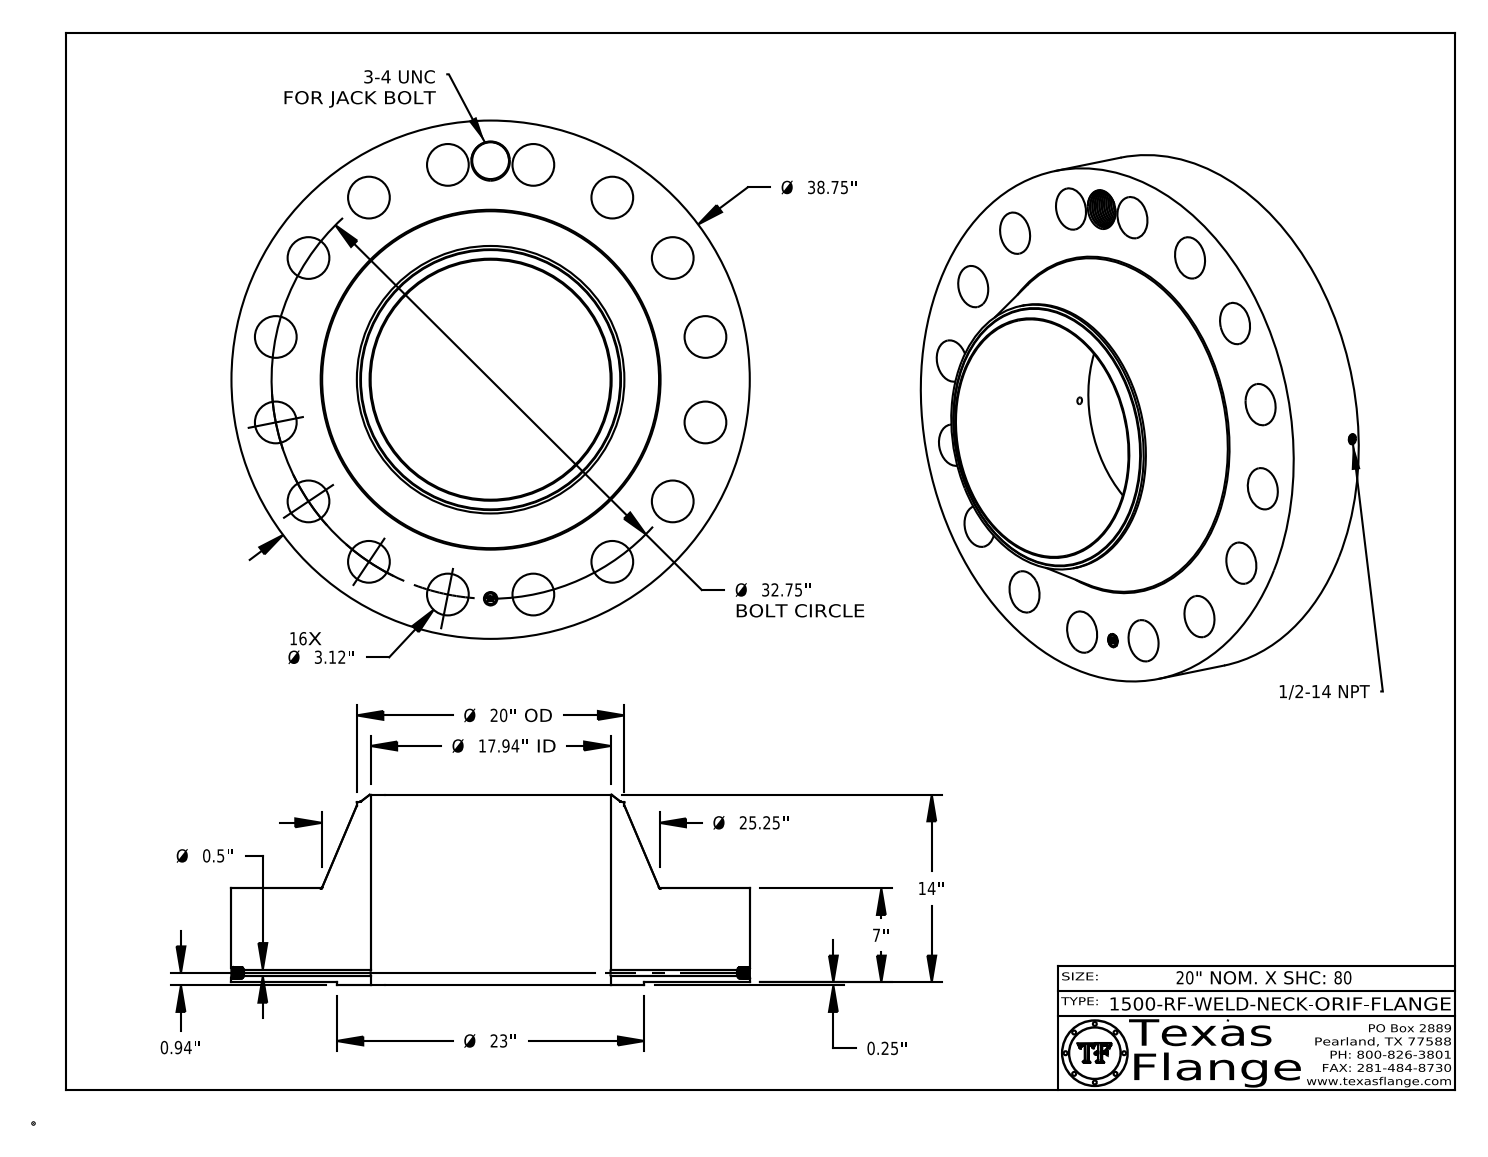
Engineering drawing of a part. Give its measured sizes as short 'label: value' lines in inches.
name: 1500-RF-WELD-NECK
written by: CATIA V5 STEP AP214 (AUTOMOTIVE_DESIGN)
unit: in
bodies: 1 solid, 867 faces (369 planar, 136 cylindrical, 362 other)
size: 38.75 × 38.75 × 14.25
volume: 6 587 in³; area: 4 808 in²
holes: 16× ⌀3.12, 1× ⌀0.5, 1× ⌀0.672, 1× ⌀1, 1× ⌀2.75, 1× ⌀17.938
bosses: 8× ⌀0.061, 1× ⌀38.75, 1× ⌀23, 1× ⌀20, 1× ⌀0.788
face distances: 7, 0.25, 7.25, 14.25, 14, 0.015, 7.235, 6.985, 7.015, 0.298
hole spacings: 30.257, 18.195, 27.231, 32.12, 16.375, 6.389, 6.389, 12.533
